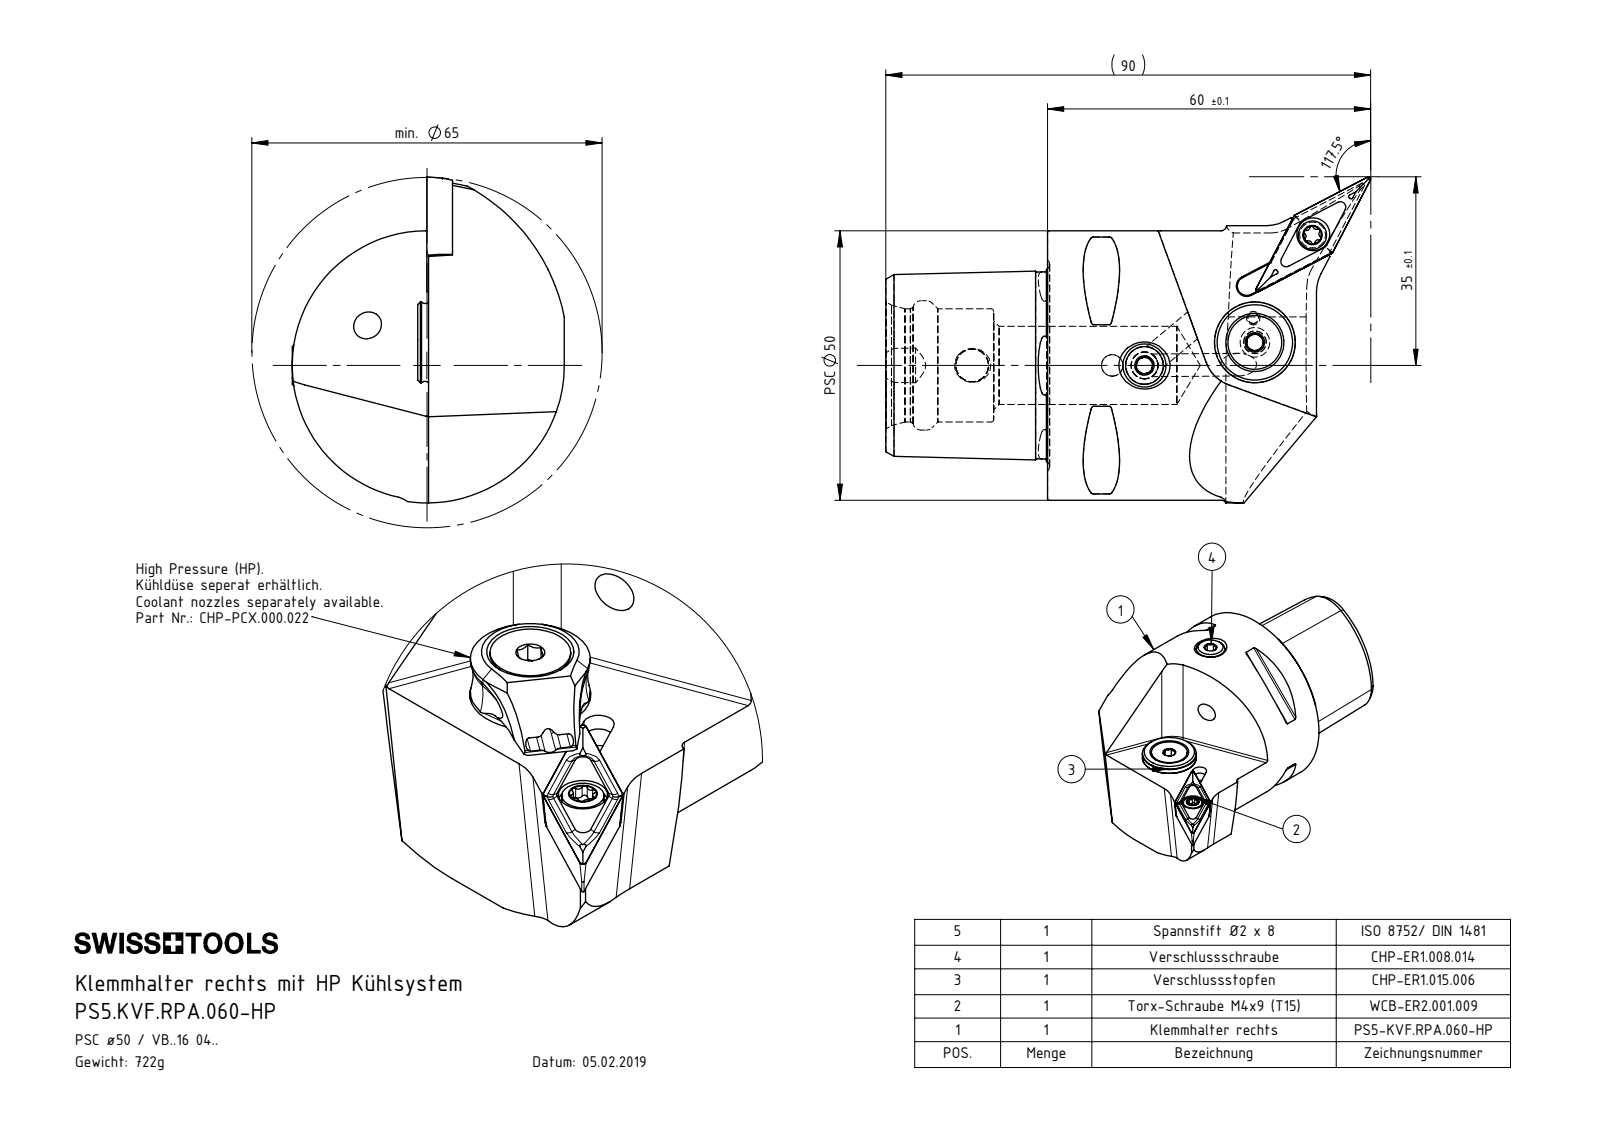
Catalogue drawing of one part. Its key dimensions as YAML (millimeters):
part_name: "ISO 8752 2x8; DIN 3771 - 6.5x1.5; WCB-ER2.001.009_A; PS5-KVF.RPA.060-HP_A (+7 more)"
step_written_by: "SolidWorks 2017 (AUTOMOTIVE_DESIGN)"
units: millimeters
bodies: {solids: 9, faces: 488, planar: 108, cylindrical: 137, other: 243}
overall_size: [90, 60.5, 50.5]
volume: 91961
surface_area: 22682
round_holes:
  - {diameter: 4.2, count: 2}
  - {diameter: 5, count: 2}
  - {diameter: 6.1, count: 2}
  - {diameter: 1.2, count: 1}
  - {diameter: 2, count: 1}
  - {diameter: 3, count: 1}
  - {diameter: 3.3, count: 1}
  - {diameter: 4, count: 1}
  - {diameter: 4.4, count: 1}
  - {diameter: 5.3, count: 1}
  - {diameter: 7, count: 1}
  - {diameter: 13, count: 1}
round_bosses_or_shafts:
  - {diameter: 50, count: 1}
  - {diameter: 14.85, count: 1}
  - {diameter: 13.4, count: 1}
  - {diameter: 10, count: 1}
  - {diameter: 8, count: 1}
  - {diameter: 5.5, count: 1}
  - {diameter: 5.25, count: 1}
  - {diameter: 5, count: 1}
partial_cylinders:
  - {radius: 0.5, count: 12}
  - {radius: 1, count: 7}
  - {radius: 0.34, count: 6}
  - {radius: 0.59, count: 6}
  - {radius: 6, count: 3}
  - {radius: 7, count: 3}
  - {radius: 0.15, count: 2}
  - {radius: 1.1, count: 2}
face_to_face_distances: [30, 4.46, 19.18, 4.5, 44.4, 20.7, 20.74, 25.2, 1.5, 3]
hole_center_spacings: [4.5, 6, 18.95, 19.16, 20.93, 22, 22.6, 22.81]
